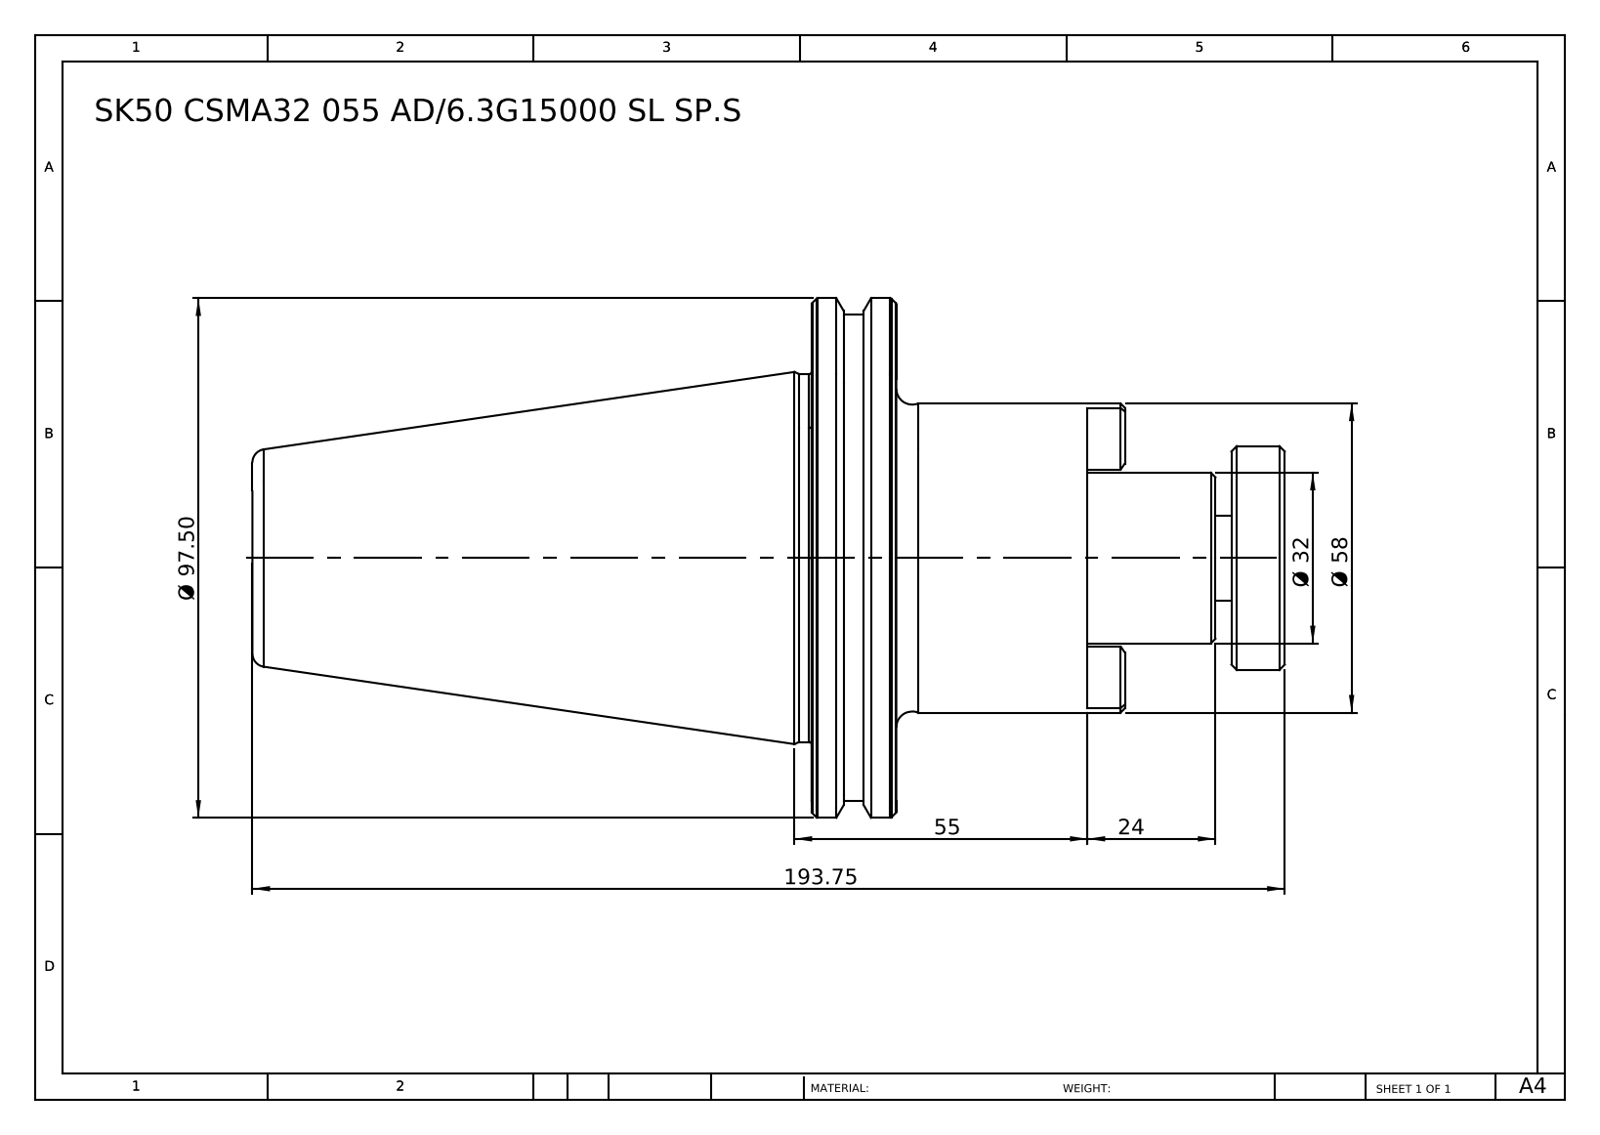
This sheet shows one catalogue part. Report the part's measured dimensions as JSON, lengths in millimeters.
{"part_name": "SK 50 CSMA32 055 AD-6.3G15000 SL SP", "step_written_by": "SolidWorks 2014 (CONFIG_CONTROL_DESIGN)", "units": "millimeters", "bodies": {"solids": 1, "faces": 121, "planar": 19, "cylindrical": 18, "other": 84}, "overall_size": [193.75, 97.5, 97.5], "volume_mm3": 504395, "surface_area_mm2": 49520, "round_bosses_or_shafts": [[97.5, 1], [91.25, 1], [69, 1], [58, 1], [42, 1], [32, 1], [16, 1]], "partial_cylinders_radius": [[18, 1]], "face_to_face_distances": [15.9, 35.9, 51.8, 37, 72.9, 88.8, 10, 27, 62.9, 78.8]}
